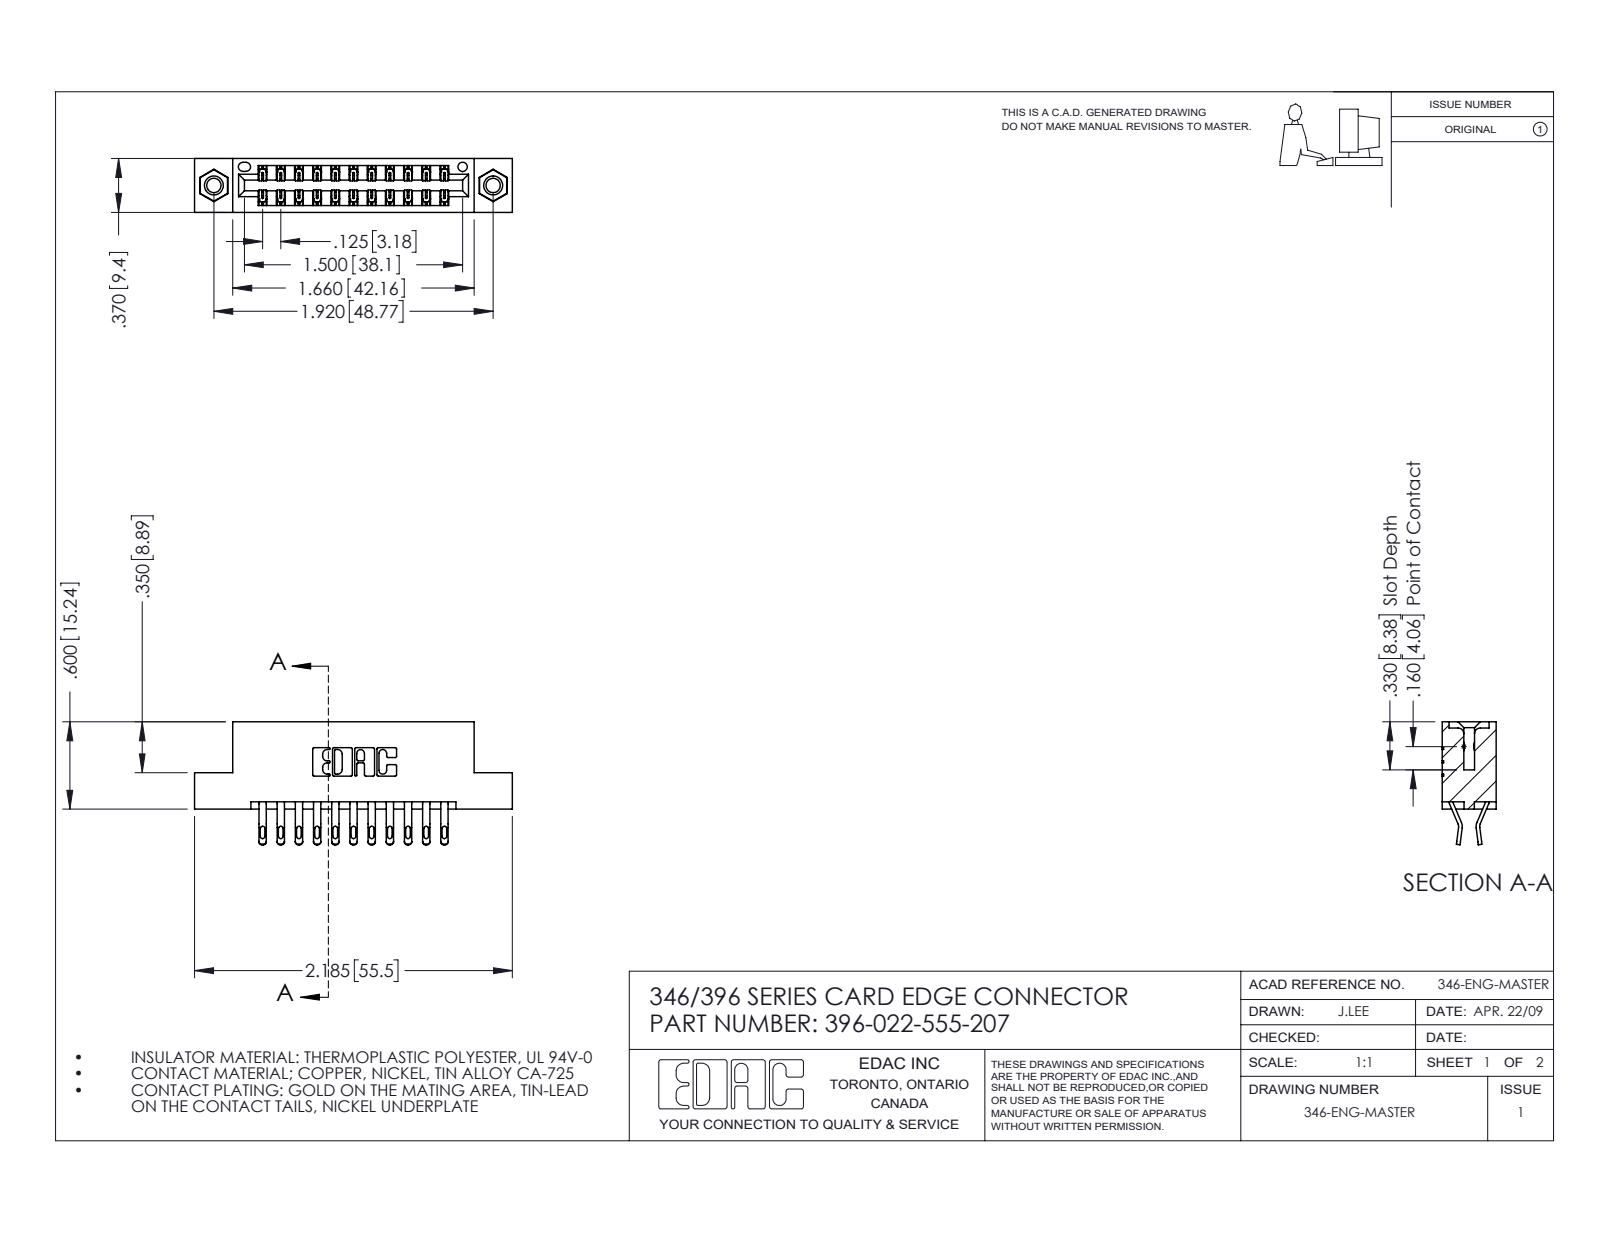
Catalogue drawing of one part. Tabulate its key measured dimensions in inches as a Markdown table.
| quantity | value |
| --- | --- |
| part name | 346 Part_Flush Mounting Lugs - 0.156 Dia-TI; 345-250-001_345-250-005-103; 345-292-001_555 Tail; 396-022-555-207 |
| STEP written by | SolidWorks 2016 (CONFIG_CONTROL_DESIGN) |
| units | inches |
| bodies | 25 solids, 1458 faces (834 planar, 608 cylindrical, 16 other) |
| overall size | 2.185 × 0.845 × 0.37 |
| volume | 0.319 in³ |
| surface area | 10.77 in² |
| round holes (diameter × count) | 0.098 × 2, 0.125 × 2, 0.156 × 2, 0.064 × 1 |
| round bosses / shafts (diameter × count) | 0.155 × 2 |
| partial cylindrical surfaces (radius × count) | 0.016 × 44, 0.02 × 44, 0.006 × 33, 0.01 × 22, 0.007 × 6, 0.031 × 6, 0.026 × 3, 0.01 × 2 |
| main face-to-face distances | 0.25, 0.048, 0.322, 0.37, 0.025, 0.072, 0.298, 0.275, 0.148, 0.222 |
| hole center spacings | 0.246, 1.715, 1.92 |
